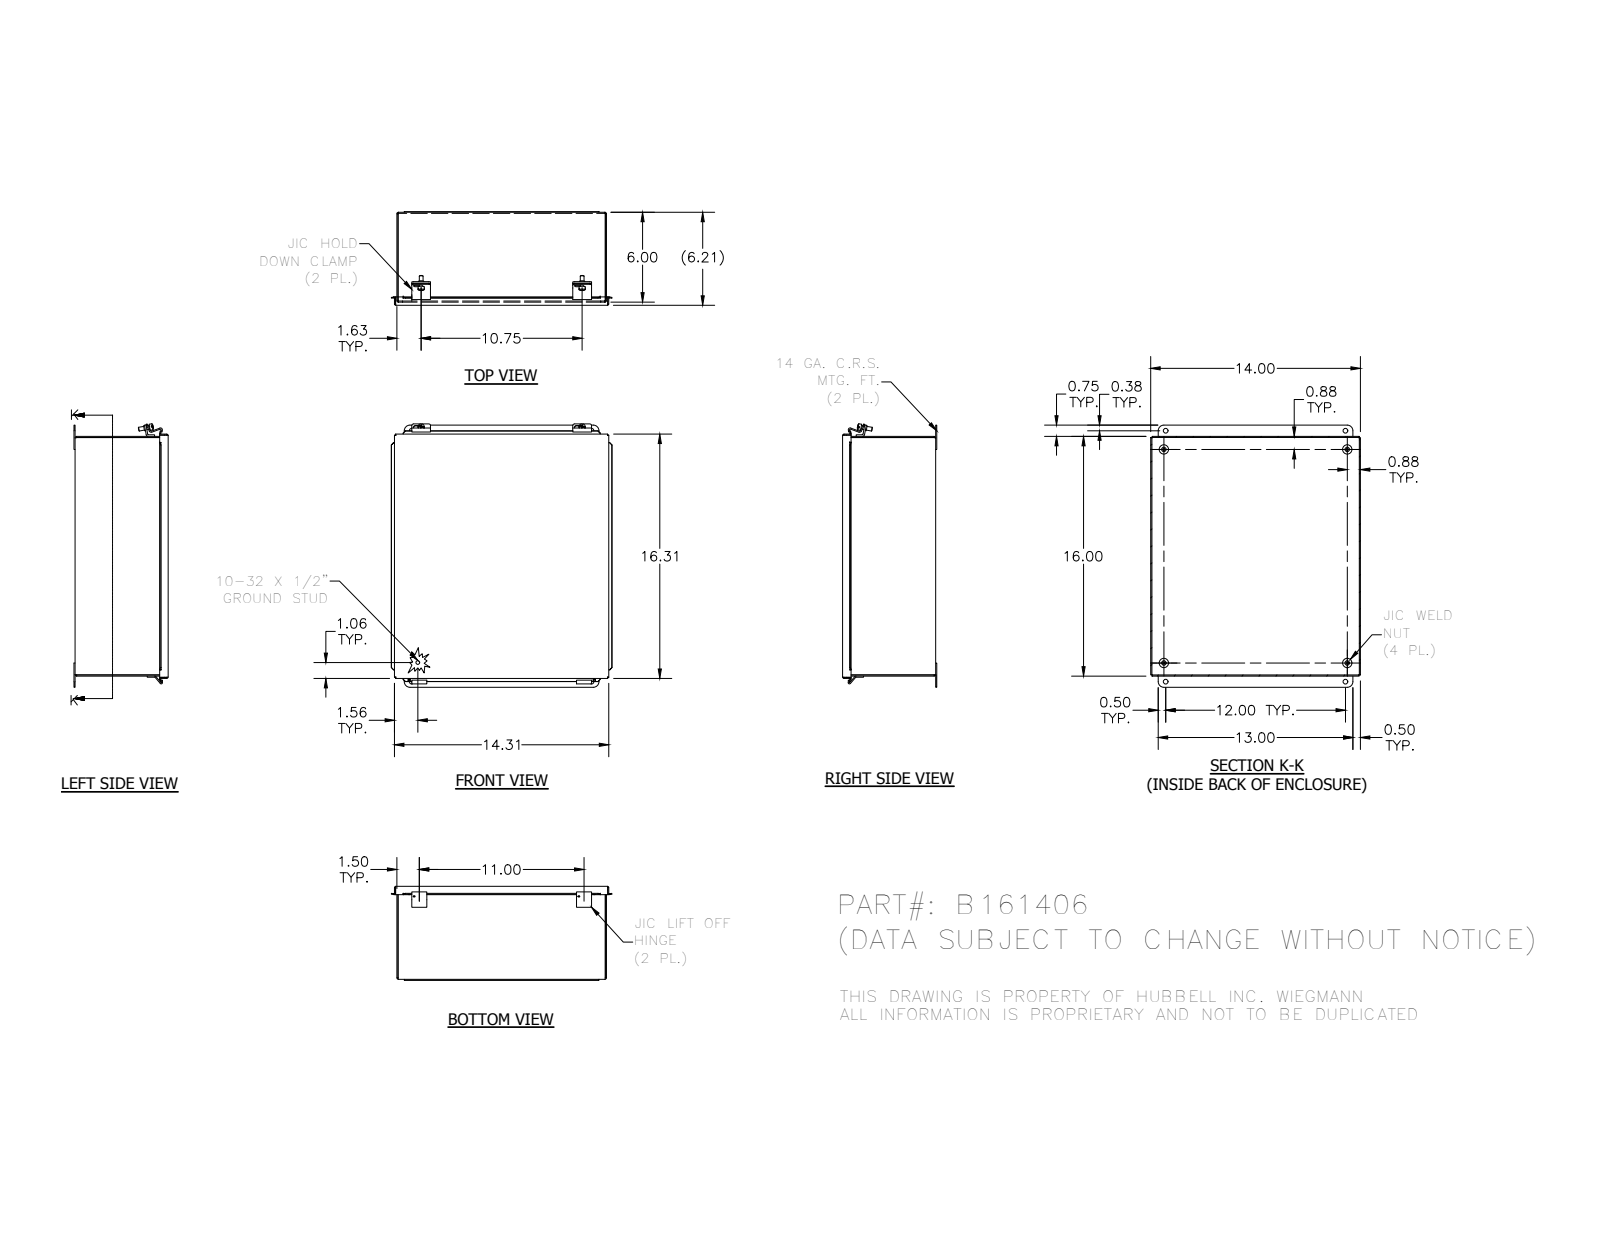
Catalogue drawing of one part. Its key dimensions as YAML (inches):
part_name: "B161406; 3499; 3486; C1001 (+7 more)"
step_written_by: "Autodesk Inventor 2012 (AUTOMOTIVE_DESIGN)"
units: inches
bodies: {solids: 19, faces: 422, planar: 279, cylindrical: 98, other: 45}
overall_size: [17.593, 14.739, 6.287]
volume: 71.65
surface_area: 1950
round_holes:
  - {diameter: 0.156, count: 4}
  - {diameter: 0.31, count: 4}
  - {diameter: 0.125, count: 2}
  - {diameter: 0.14, count: 2}
  - {diameter: 0.196, count: 2}
round_bosses_or_shafts:
  - {diameter: 0.625, count: 4}
  - {diameter: 0.3, count: 4}
  - {diameter: 0.25, count: 3}
  - {diameter: 0.41, count: 2}
  - {diameter: 0.344, count: 2}
  - {diameter: 0.19, count: 1}
partial_cylinders:
  - {radius: 0.031, count: 16}
  - {radius: 0.093, count: 8}
  - {radius: 0.105, count: 8}
  - {radius: 0.125, count: 8}
  - {radius: 0.133, count: 4}
  - {radius: 0.375, count: 4}
  - {radius: 0.063, count: 3}
  - {radius: 0.126, count: 3}
face_to_face_distances: [0.074, 6.15, 0.062, 6.212, 6.076, 6.138, 13.926, 15.926, 13.852, 14]
hole_center_spacings: [12.189, 1.256, 12, 12.25, 14.25, 15.5, 16.75, 16.768]
